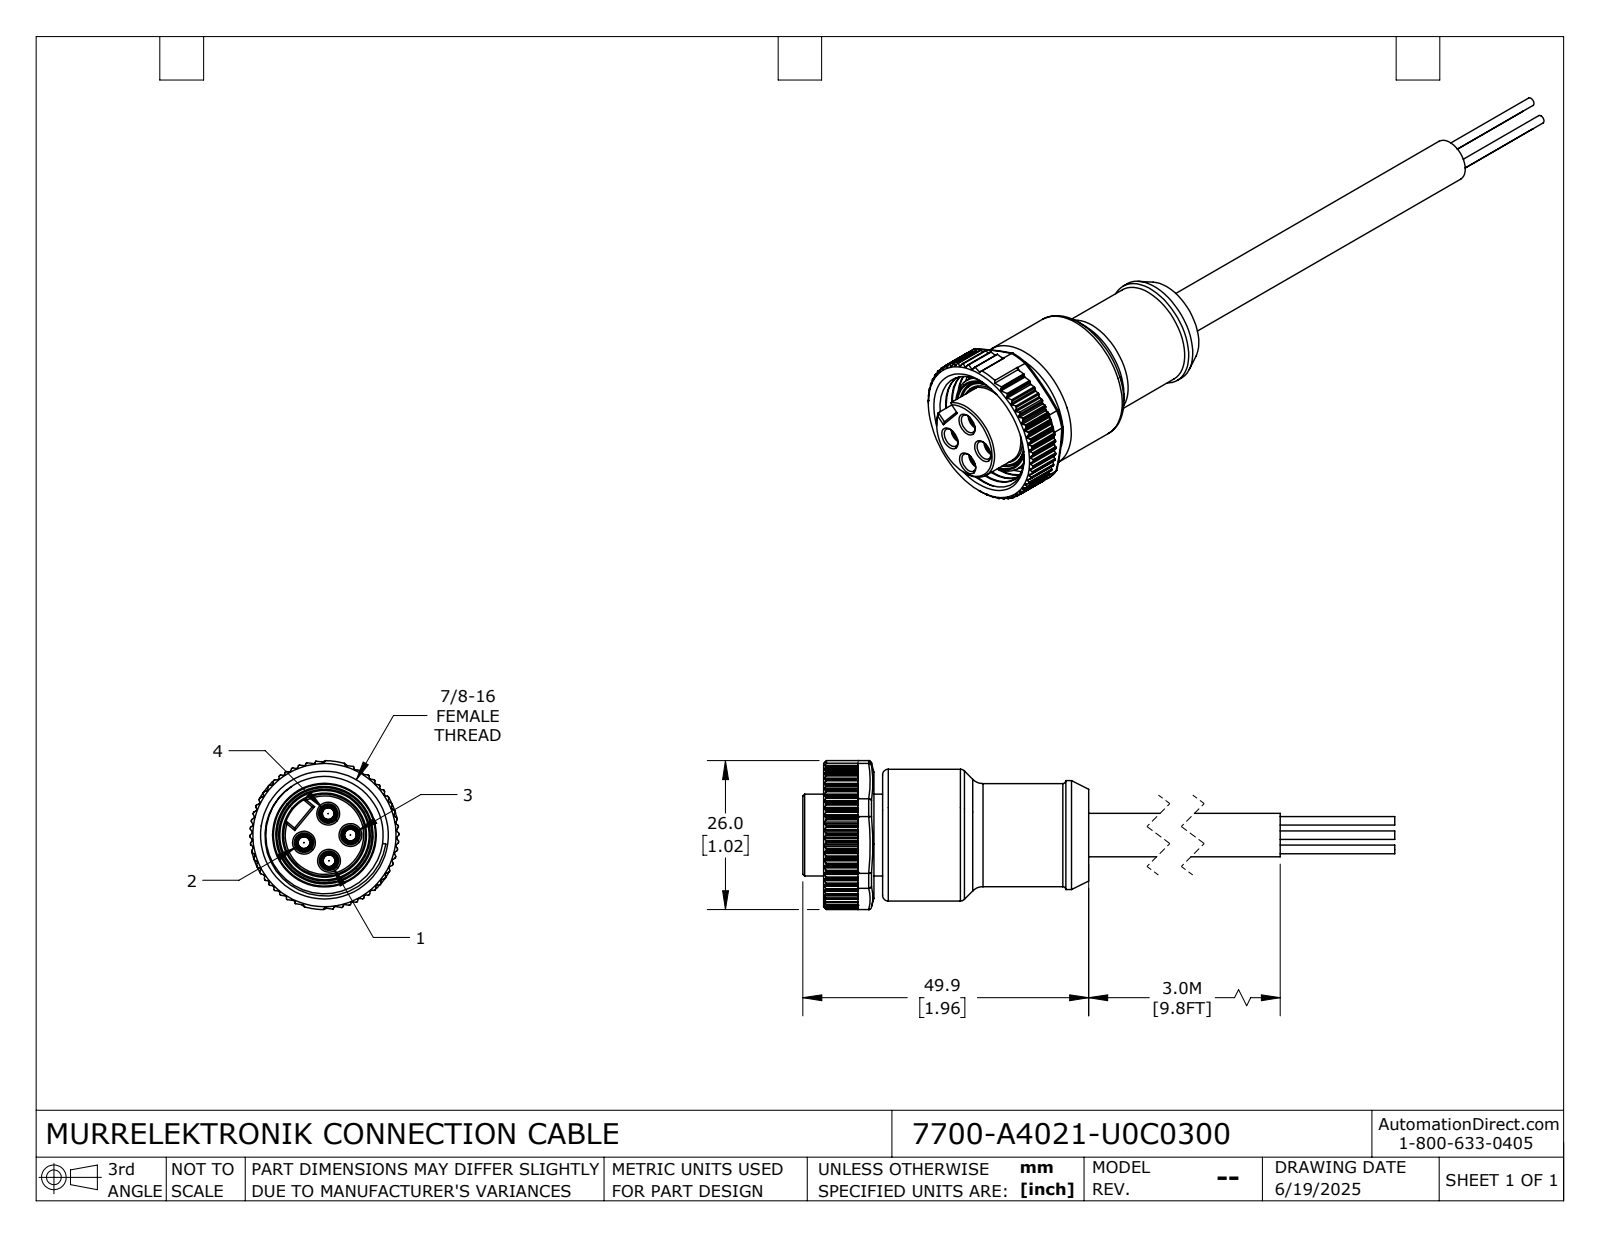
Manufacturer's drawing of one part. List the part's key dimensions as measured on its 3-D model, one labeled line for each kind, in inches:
Part name (STEP PRODUCT): 7700-A4021-U0C0300
STEP written by: SolidWorks 2024 (CONFIG_CONTROL_DESIGN)
Units: inches
Bodies: 1 solid, 674 faces (296 planar, 293 cylindrical, 85 other)
Overall size (bounding box): 5.508 × 1.024 × 1.024
Volume: 1.146 in³ · Surface area: 12.9 in²
Round holes (diameter × count): ⌀0.081 ×4, ⌀0.118 ×4, ⌀0.134 ×4, ⌀0.61 ×1, ⌀0.614 ×1, ⌀0.807 ×1, ⌀0.875 ×1
Round bosses / shafts (diameter × count): ⌀0.059 ×4, ⌀0.906 ×1, ⌀0.748 ×1, ⌀0.713 ×1, ⌀0.709 ×1, ⌀0.701 ×1, ⌀0.563 ×1, ⌀0.299 ×1
Partial cylindrical surfaces — rounded edges, fillets, slot ends (radius × count): R0.008 ×126, R0.012 ×16, R0.004 ×4, R0.029 ×4, R0.512 ×1
Main face-to-face distances: 0.059, 1.476, 1.417, 0.142, 0.346, 0.406, 1.823, 0.488, 0.547, 1.965
Hole centre spacings: 0.15, 0.179, 0.324, 0.212, 0.213, 0.23, 0.26
